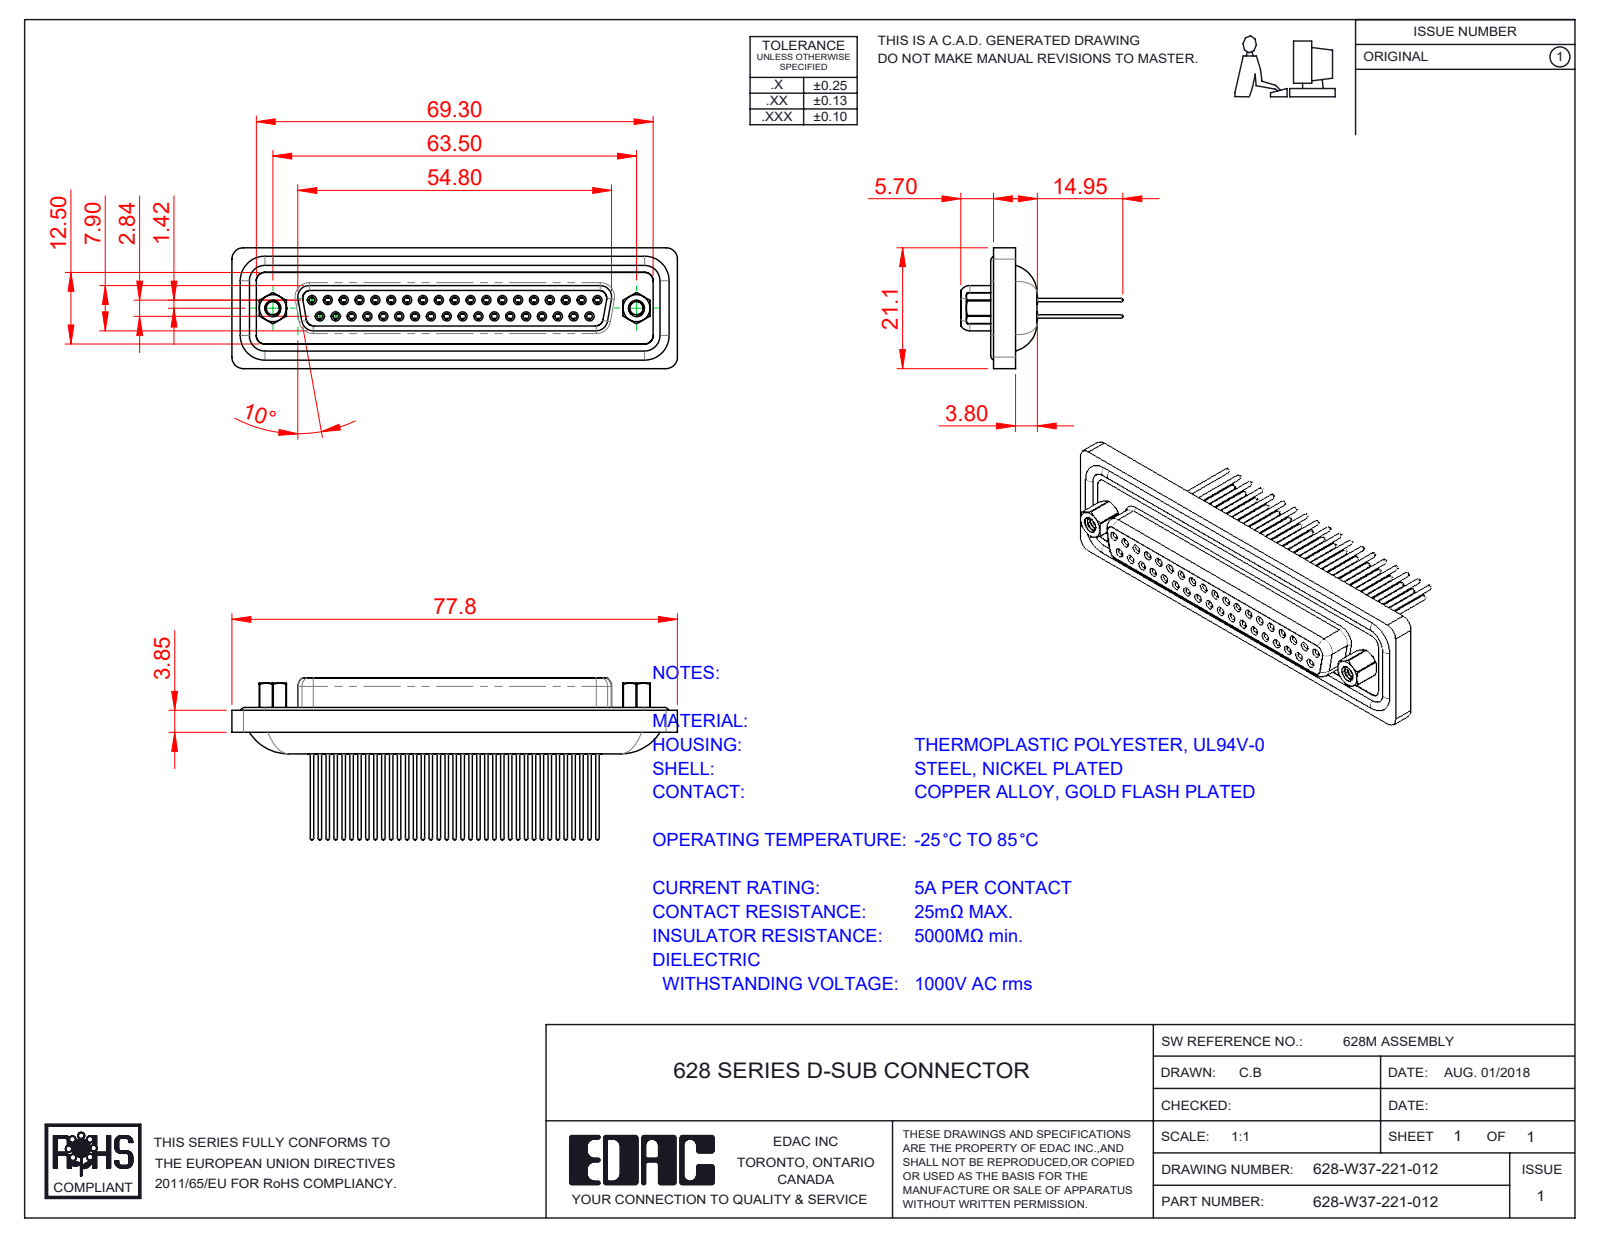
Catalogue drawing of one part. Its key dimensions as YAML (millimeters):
part_name: "628W Contact Row 2_21; 628W Shell Front_37 Contacts; 628W Housing_37 Contacts; 628W Waterproof Housing_37 Contacts (+4 more)"
step_written_by: "SolidWorks 2020 (CONFIG_CONTROL_DESIGN)"
units: millimeters
bodies: {solids: 45, faces: 2532, planar: 656, cylindrical: 997, other: 879}
overall_size: [77.8, 28.3, 21.1]
volume: 11160
surface_area: 18575
round_holes:
  - {diameter: 1, count: 37}
  - {diameter: 1.1, count: 37}
  - {diameter: 1.5, count: 37}
  - {diameter: 1.7, count: 37}
  - {diameter: 1.8, count: 37}
  - {diameter: 2, count: 37}
  - {diameter: 2.26, count: 2}
  - {diameter: 2.29, count: 2}
  - {diameter: 4, count: 2}
  - {diameter: 4.8, count: 2}
  - {diameter: 5, count: 2}
round_bosses_or_shafts:
  - {diameter: 1.6, count: 41}
  - {diameter: 2.2, count: 37}
  - {diameter: 0.6, count: 37}
  - {diameter: 1.5, count: 8}
  - {diameter: 4.9, count: 2}
  - {diameter: 2.79, count: 2}
partial_cylinders:
  - {radius: 2, count: 16}
  - {radius: 1.5, count: 14}
  - {radius: 1.35, count: 8}
  - {radius: 2.7, count: 6}
  - {radius: 0.5, count: 4}
  - {radius: 0.9, count: 4}
  - {radius: 1.6, count: 4}
  - {radius: 1.75, count: 4}
face_to_face_distances: [0.4, 7.45, 7.5, 8.45, 6.2, 13.65, 3.75, 4.1, 1.1, 2.75]
hole_center_spacings: [3.16, 2.77, 5.54, 8.31, 5.04, 7.49, 11.08, 13.85]
